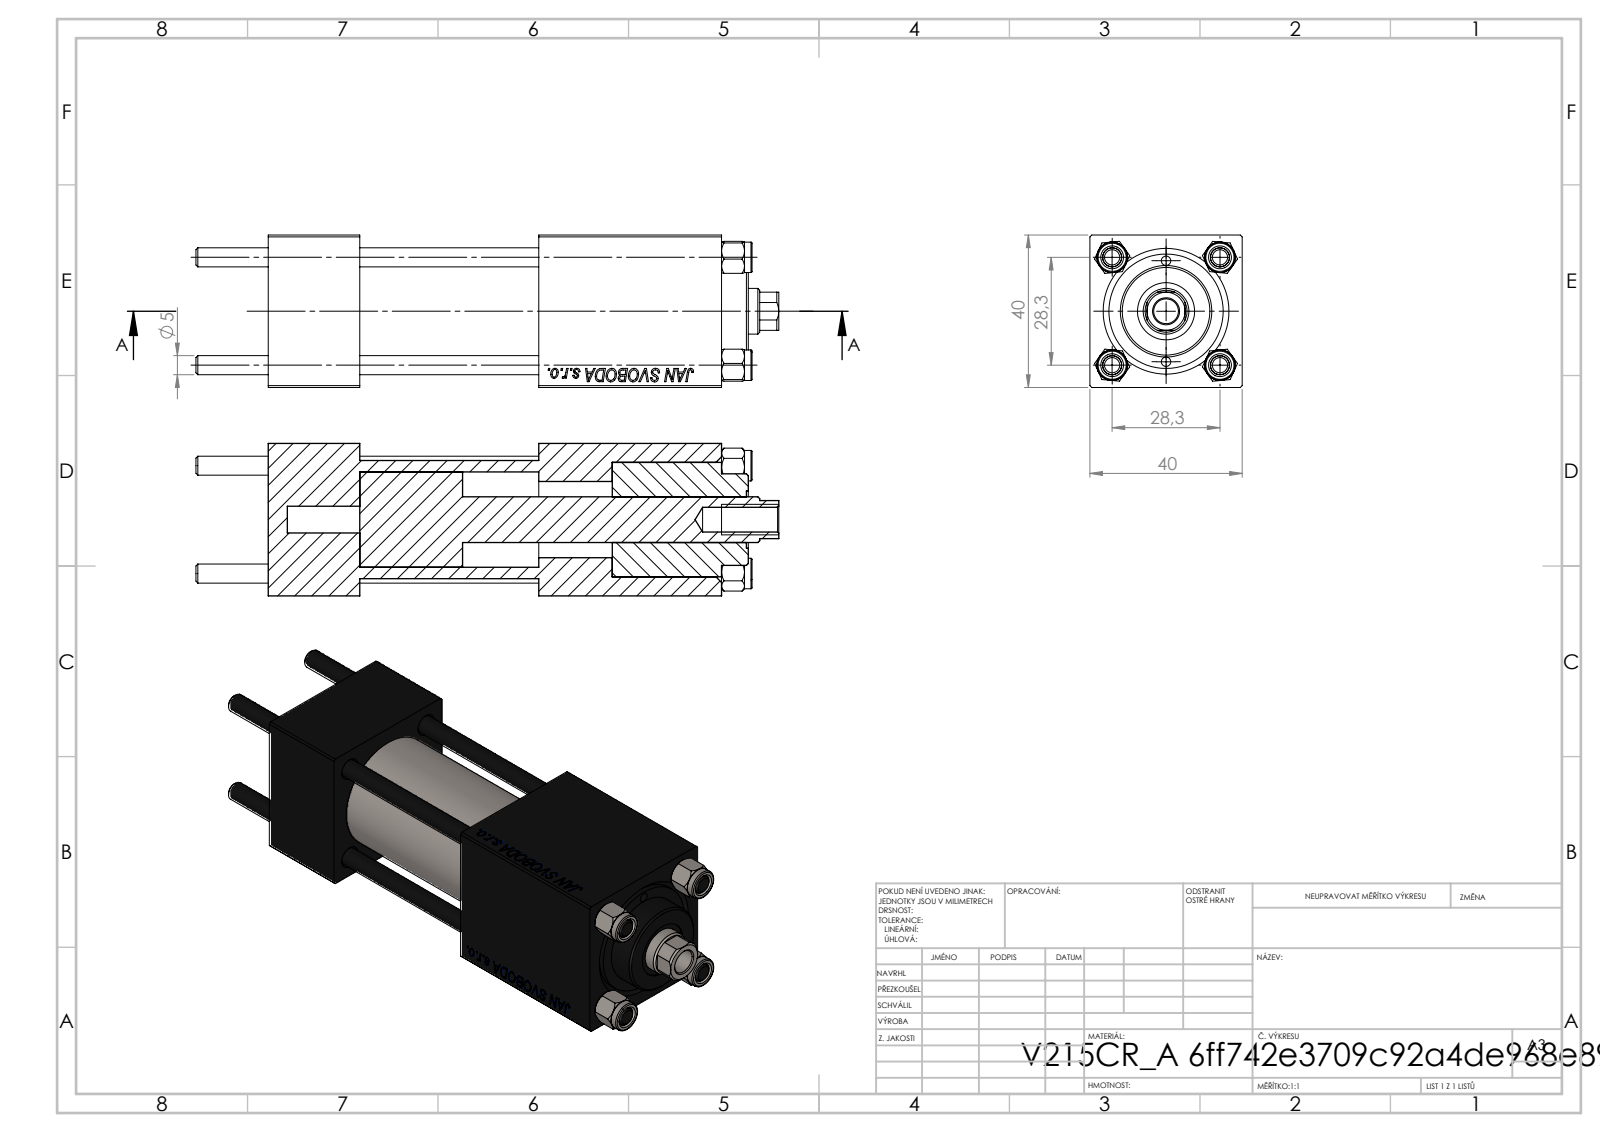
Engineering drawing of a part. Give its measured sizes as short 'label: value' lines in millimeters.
name: V215CR_BODY_A; NUT_M5; V215CR_VCP; V215_VC_A (+1 more)
written by: SolidWorks 2019 (CONFIG_CONTROL_DESIGN)
unit: mm
bodies: 11 solids, 1137 faces (519 planar, 82 cylindrical, 536 other)
size: 153 × 40 × 40
volume: 144 775 mm³; area: 58 950 mm²
holes: 4× ⌀5, 3× ⌀20, 2× ⌀2.5, 2× ⌀7, 2× ⌀13.16, 1× ⌀6.5, 1× ⌀12, 1× ⌀15, 1× ⌀25, 1× ⌀30
bosses: 4× ⌀8, 1× ⌀31, 1× ⌀24
rounds: 1× R5.5
face distances: 40, 24, 90.3, 66.3, 119, 95, 28.7, 71, 47, 19.3
hole spacings: 14.18, 20.01, 28.3, 30.84, 13.25, 40.02, 26.5, 72
